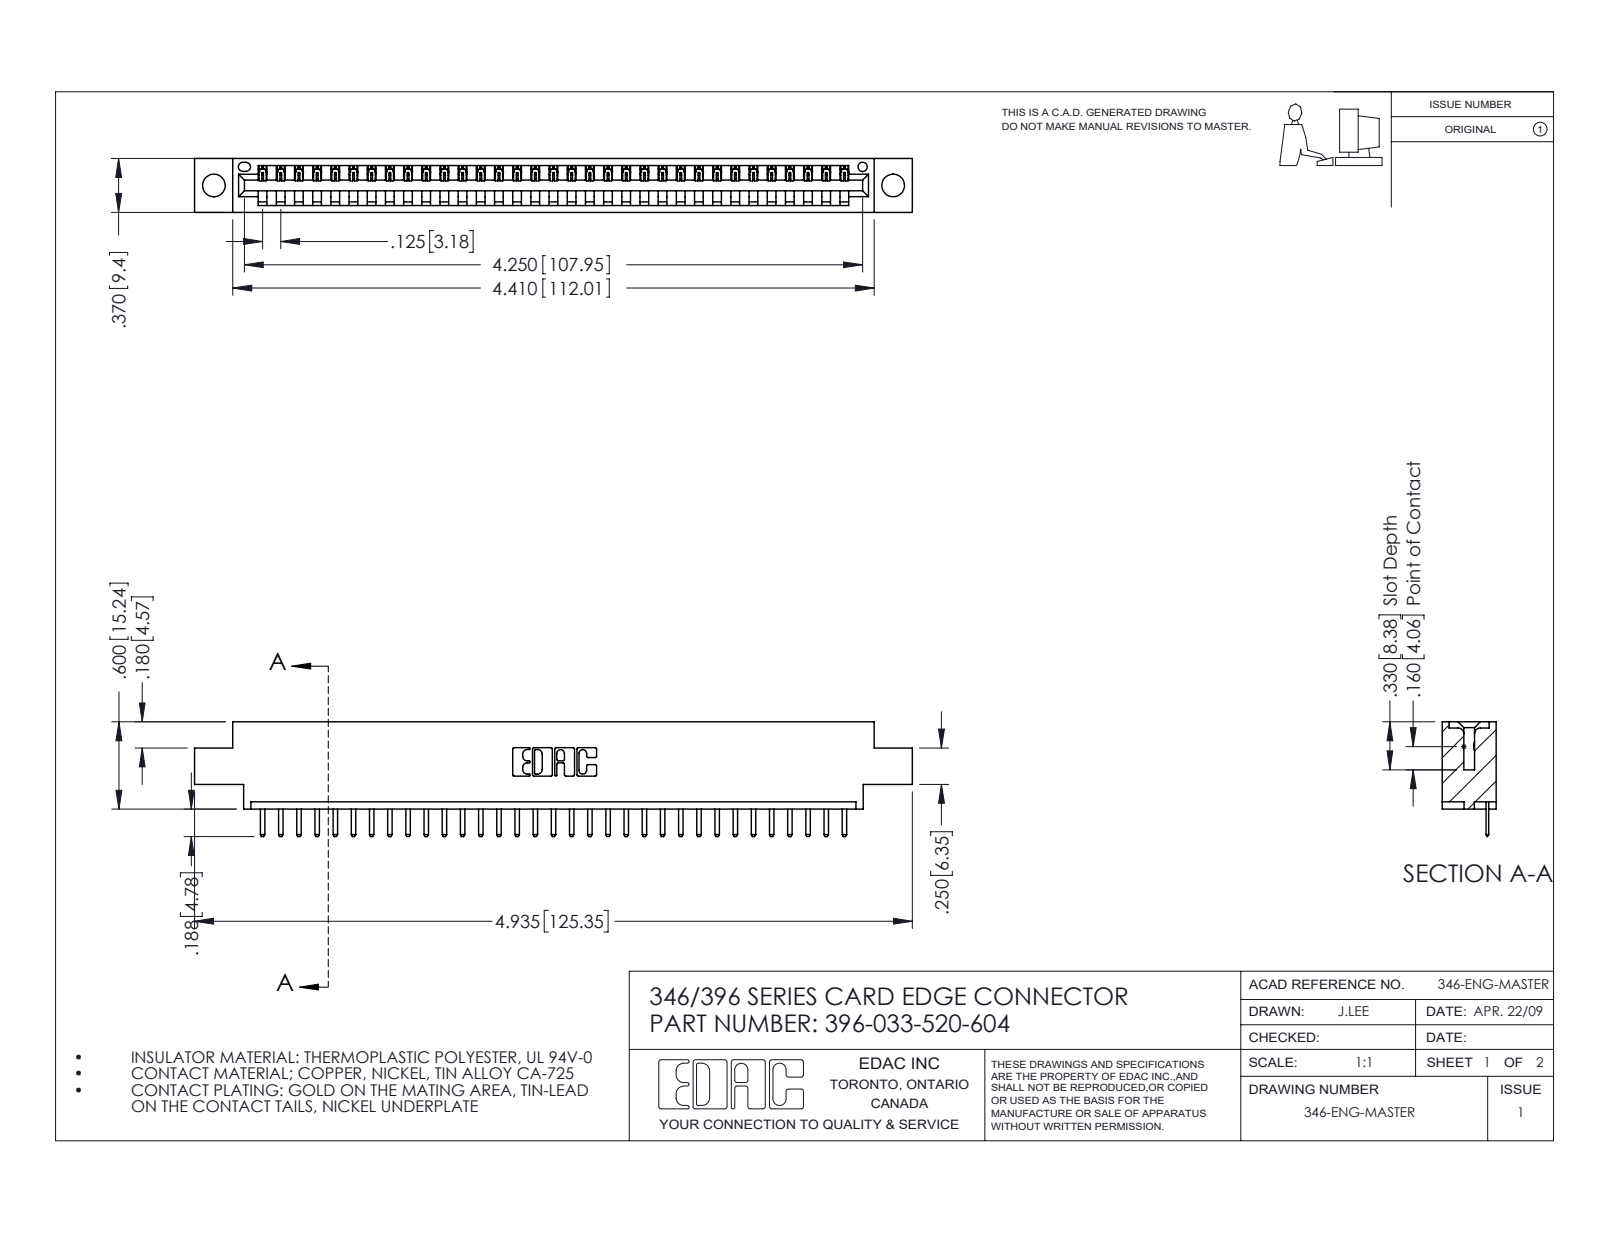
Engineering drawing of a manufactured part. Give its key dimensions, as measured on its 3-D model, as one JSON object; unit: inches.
{"part_name": "345-292-001_345-293-120; 346 Part_0.170 Offset - 0.156 Dia-TH; 396-033-520-604", "step_written_by": "SolidWorks 2016 (CONFIG_CONTROL_DESIGN)", "units": "inches", "bodies": {"solids": 34, "faces": 2172, "planar": 1466, "cylindrical": 706, "other": 0}, "overall_size": [4.935, 0.788, 0.37], "volume_in3": 0.708, "surface_area_in2": 21.78, "round_holes": [[0.156, 2], [0.064, 1]], "partial_cylinders_radius": [[0.01, 68], [0.006, 66], [0.01, 22], [0.007, 6], [0.031, 6], [0.026, 3], [0.031, 2], [0.04, 2]], "face_to_face_distances": [0.048, 0.322, 0.37, 0.25, 0.148, 0.222, 0.1, 0.174, 0.072, 0.298], "hole_center_spacings": [0.246, 4.462, 4.67]}
